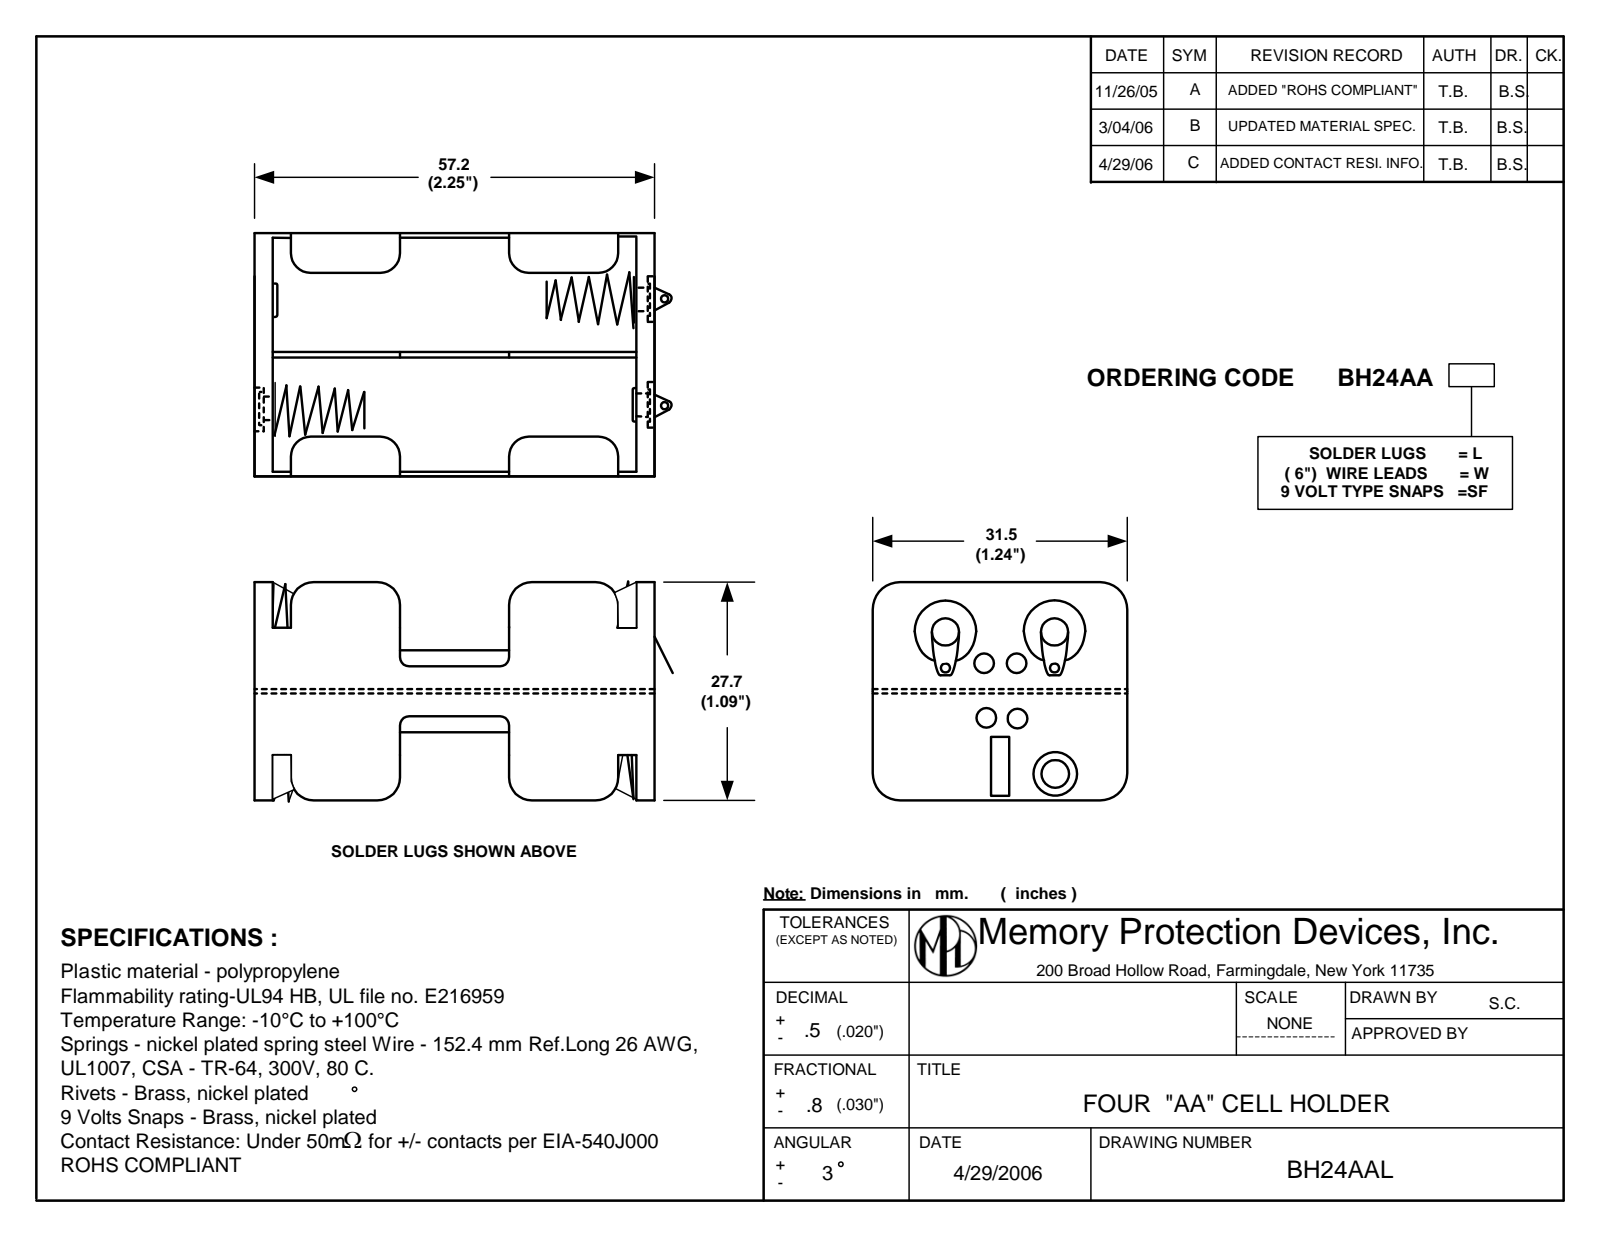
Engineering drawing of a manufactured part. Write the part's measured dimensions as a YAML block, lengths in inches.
part_name: "BH24AAL"
step_written_by: "SolidWorks 2017 (AUTOMOTIVE_DESIGN)"
units: inches
bodies: {solids: 9, faces: 650, planar: 232, cylindrical: 256, other: 162}
overall_size: [2.359, 1.22, 1.091]
volume: 0.625
surface_area: 21.92
round_holes:
  - {diameter: 0.087, count: 4}
  - {diameter: 0.091, count: 4}
  - {diameter: 0.118, count: 4}
  - {diameter: 0.146, count: 4}
  - {diameter: 0.299, count: 4}
  - {diameter: 0.063, count: 3}
  - {diameter: 0.028, count: 2}
round_bosses_or_shafts:
  - {diameter: 0.244, count: 4}
  - {diameter: 0.185, count: 4}
  - {diameter: 0.024, count: 4}
  - {diameter: 0.138, count: 2}
partial_cylinders:
  - {radius: 0.008, count: 24}
  - {radius: 0.098, count: 16}
  - {radius: 0.118, count: 6}
  - {radius: 0.163, count: 4}
  - {radius: 0.17, count: 4}
  - {radius: 0.059, count: 2}
  - {radius: 0.069, count: 1}
  - {radius: 0.354, count: 1}
face_to_face_distances: [0.043, 0.589, 0.122, 2.209, 0.632, 1.177, 0.545, 1.22, 2.165, 2.252]
hole_center_spacings: [0.284, 0.382, 0.463, 0.528, 0.5, 0.13, 0.209, 0.246]
